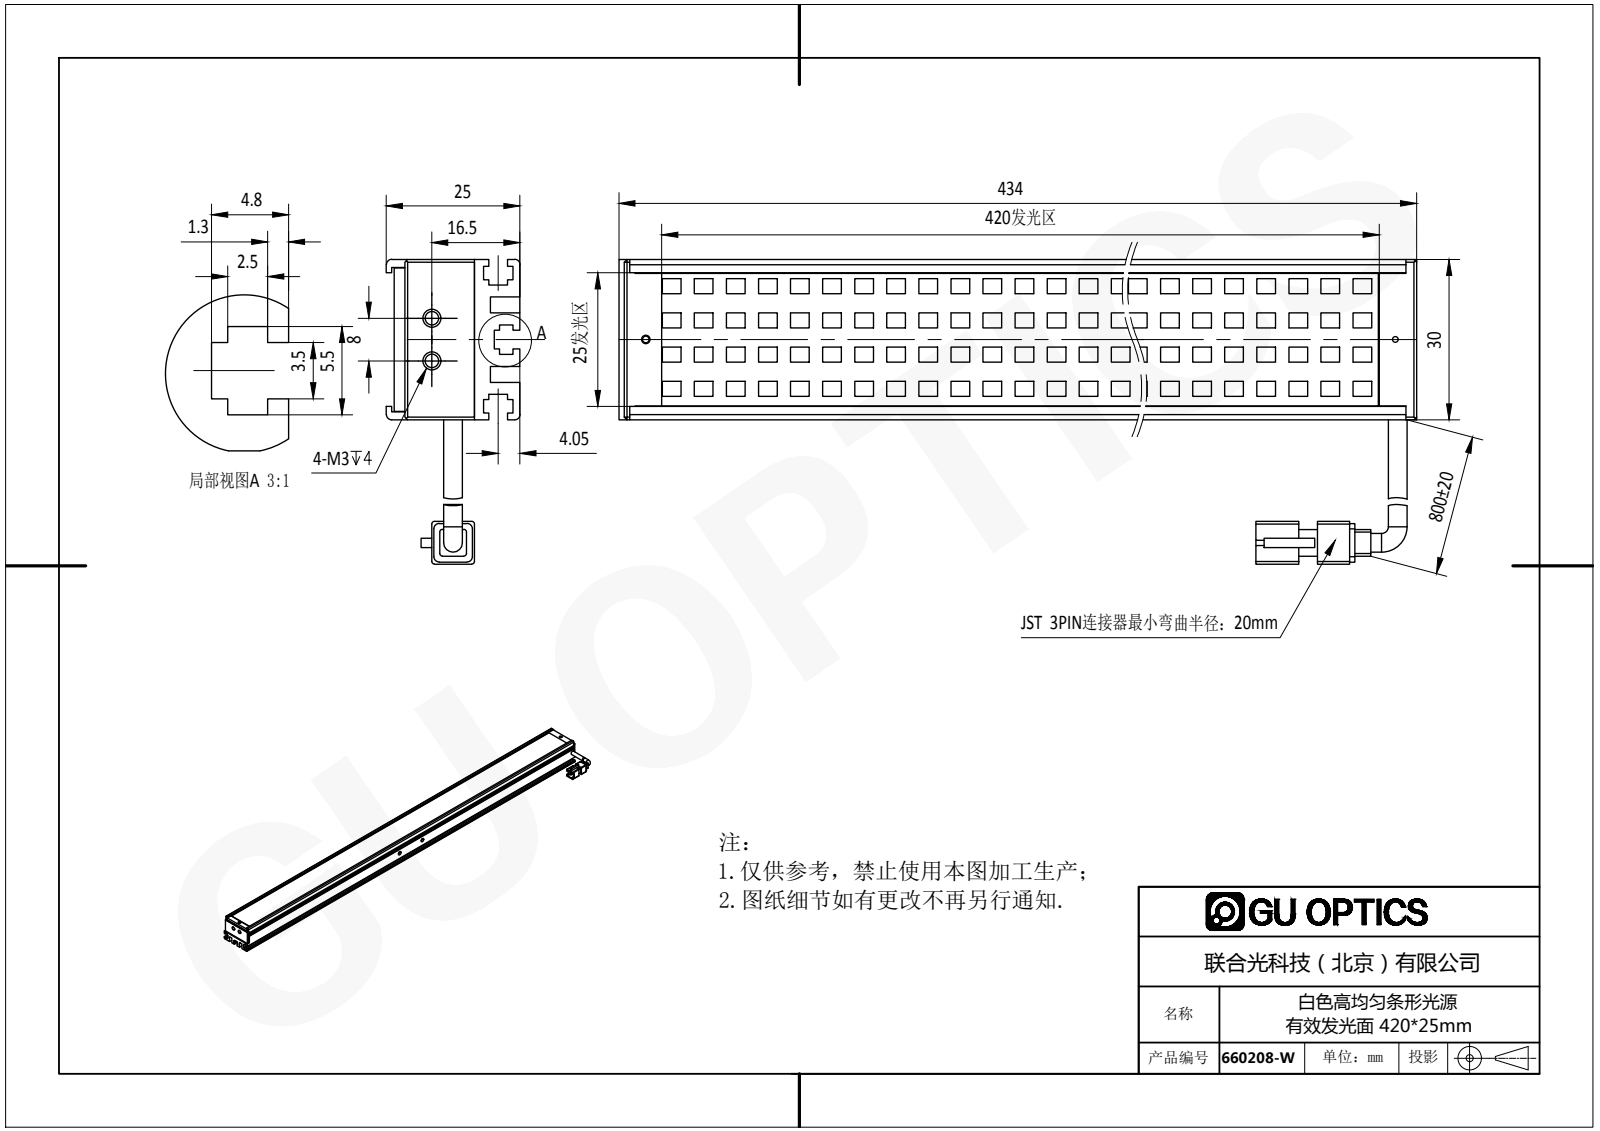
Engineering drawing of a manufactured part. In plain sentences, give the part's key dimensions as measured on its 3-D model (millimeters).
The part is named "660208-W". Its 3-D file was written by "SolidWorks 2016 (AUTOMOTIVE_DESIGN)". It is 6 solids with 1842 faces: 1656 planar, 83 cylindrical and 103 other. Overall it measures 434 by 57 by 25 millimeters. Its volume is 145 249 cubic millimeters and its surface area 148 514 square millimeters. Round holes: 5 of diameter 1.6, 2 of diameter 1.5, 2 of diameter 1.7, 2 of diameter 2.5, 2 of diameter 2.8, 2 of diameter 3, 1 of diameter 1.1, 1 of diameter 1.25, 1 of diameter 2. Round bosses or shafts: 2 of diameter 3.5. Partial cylindrical surfaces (rounded edges, fillets, slot ends): 12 of radius 1, 8 of radius 0.5, 1 of radius 1.65. The main face-to-face distances are 1, 2, 13, 2.5, 3, 27.5, 9.5, 4.5, 12, 15.1. The hole center spacings are 425, 7, 425.06, 8, 30, 197, 197.11, 198.
